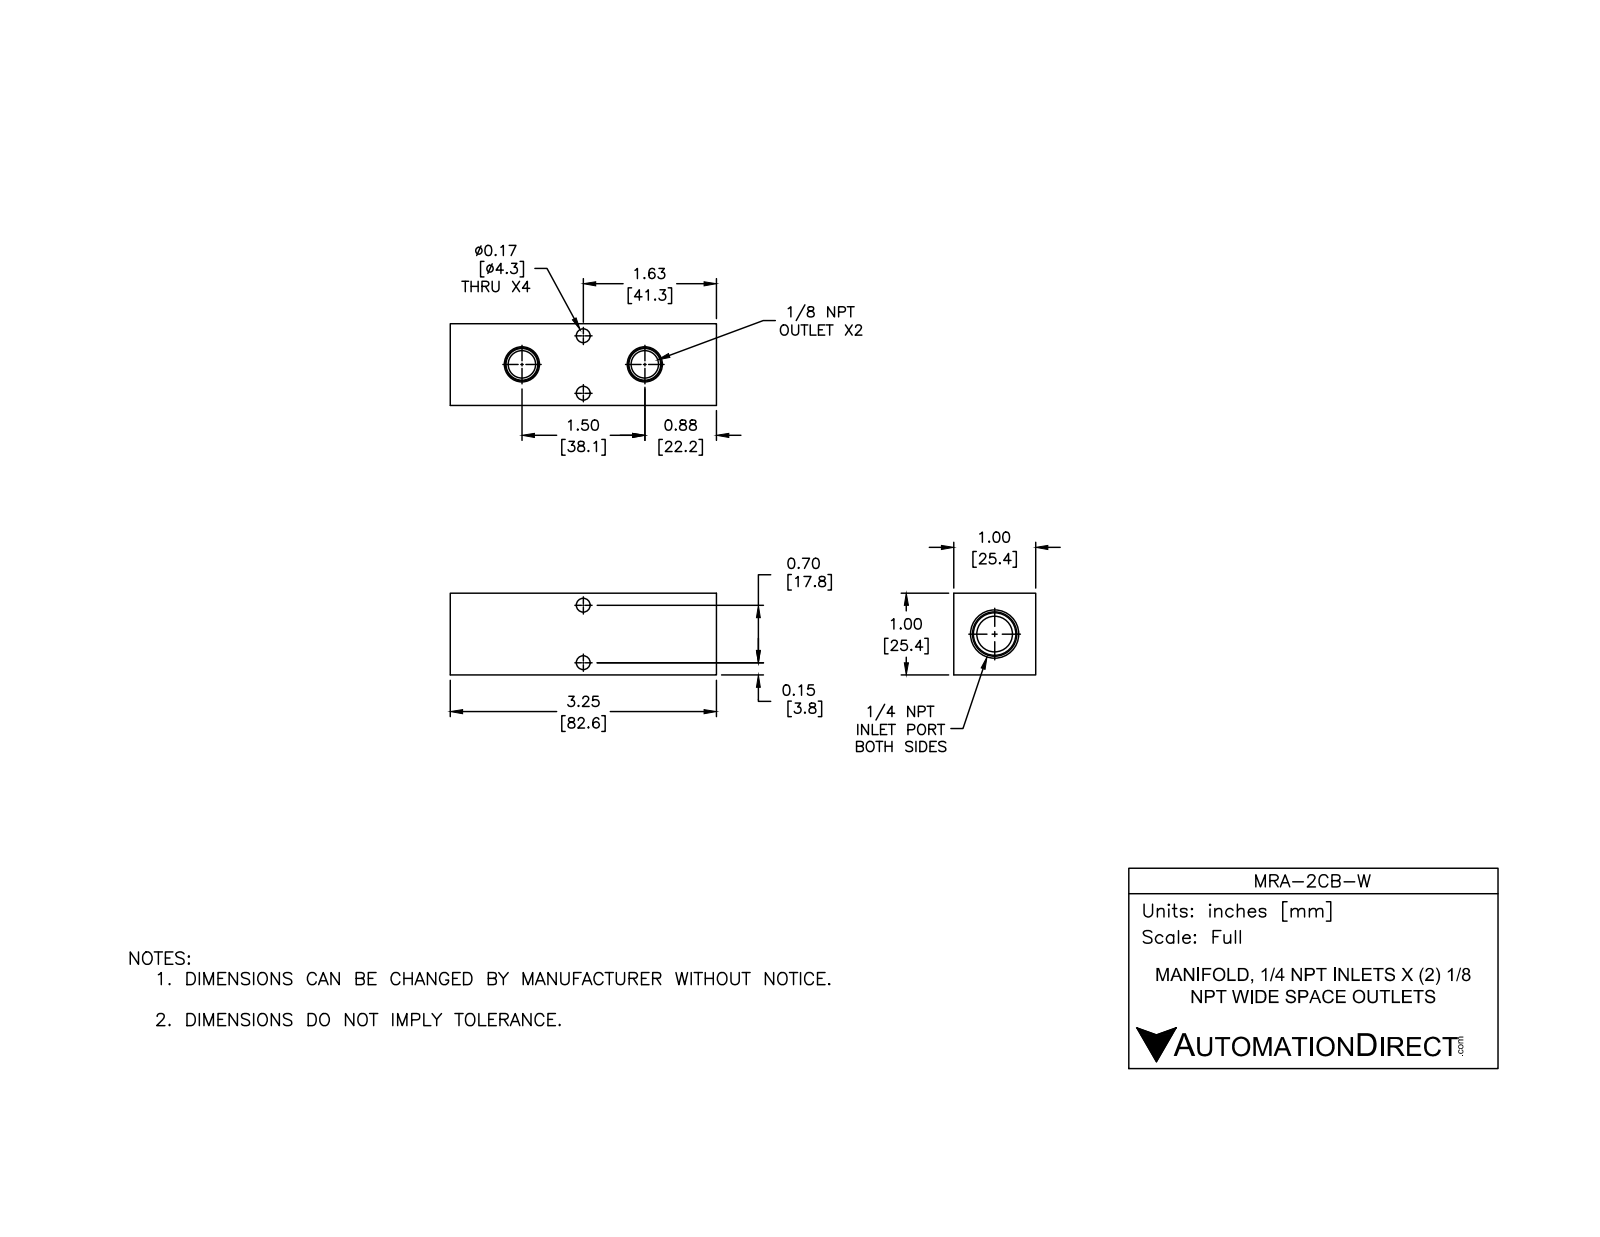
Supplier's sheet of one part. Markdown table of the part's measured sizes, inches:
| quantity | value |
| --- | --- |
| part name | MRA-2CB-W |
| STEP written by | SolidWorks 2021 (CONFIG_CONTROL_DESIGN) |
| units | inches |
| bodies | 1 solid, 56 faces (10 planar, 30 cylindrical, 16 other) |
| overall size | 3.25 × 1 × 1 |
| volume | 2.555 in³ |
| surface area | 21.18 in² |
| round holes (diameter × count) | 0.17 × 4, 0.332 × 2, 0.438 × 1 |
| main face-to-face distances | 1, 3.25, 0.39, 2.86, 0.73, 0.27, 2.47 |
| hole center spacings | 0.828, 0.7, 1.5 |
